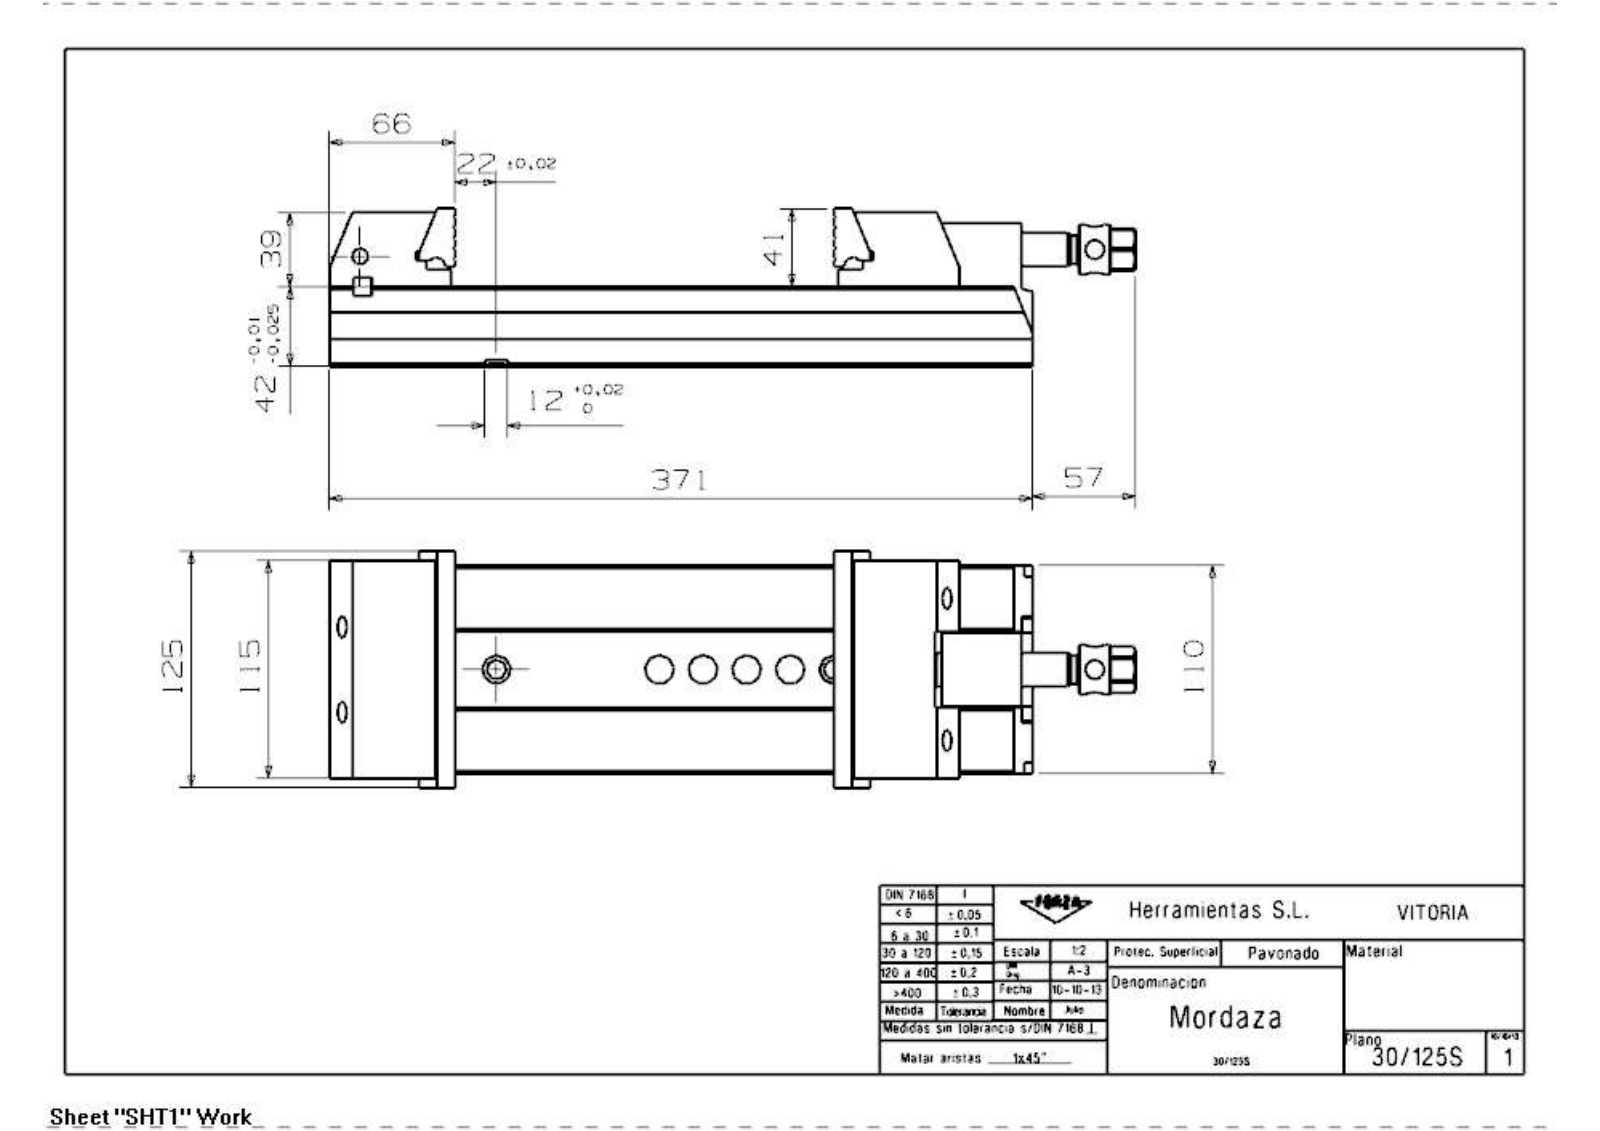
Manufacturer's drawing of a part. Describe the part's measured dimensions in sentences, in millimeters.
The part is named "30_125S_Mordaza". Its 3-D file was written by "SIEMENS PLM Software NX 1969 (AP203_CONFIGURATION_CONTROLLED_3D_DESIGN_OF_MECHANICAL_PARTS_AND_ASSEMBLIES_MIM_LF)". It is 12 solids with 516 faces: 320 planar, 147 cylindrical and 49 other. Overall it measures 425.31 by 125 by 83 millimeters. Its volume is 1 842 000 cubic millimeters and its surface area 316 487 square millimeters. Round holes: 5 of diameter 4.35, 4 of diameter 5.19, 4 of diameter 6.5, 4 of diameter 7.5, 4 of diameter 11.5, 4 of diameter 15, 3 of diameter 8.78, 2 of diameter 6.99, 2 of diameter 8, 2 of diameter 10, 2 of diameter 10.5, 2 of diameter 11. Round bosses or shafts: 1 of diameter 26, 1 of diameter 17.73, 1 of diameter 15, 1 of diameter 14.5, 1 of diameter 10.5. Partial cylindrical surfaces (rounded edges, fillets, slot ends): 20 of radius 0.3, 7 of radius 6, 4 of radius 10, 4 of radius 16, 2 of radius 1.6, 2 of radius 5, 1 of radius 3, 1 of radius 8. The main face-to-face distances are 42, 15.4, 26.6, 27, 8.5, 77, 29.5, 39, 83, 13.5. The hole center spacings are 60, 9.19, 15, 23.45, 23.76, 25.1, 38.08, 44.
